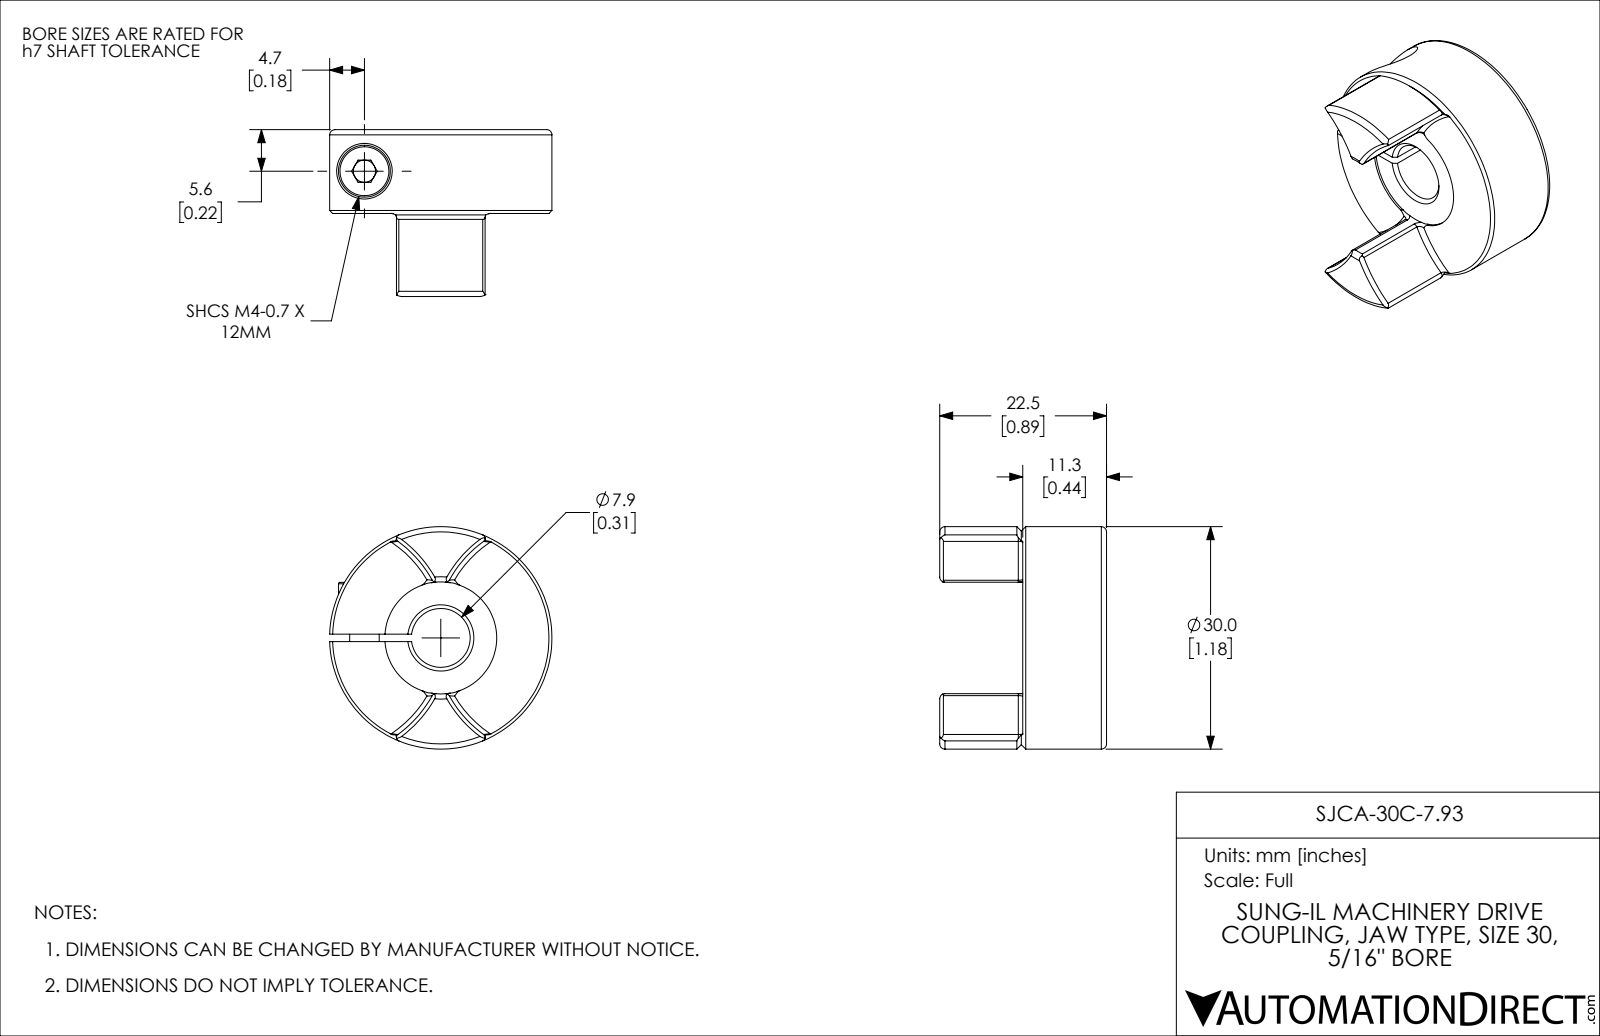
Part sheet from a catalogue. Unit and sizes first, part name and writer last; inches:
Units: inches
Overall size (bounding box): 1.181 × 1.181 × 0.886
Round holes (diameter × count): ⌀0.118 ×1, ⌀0.13 ×1, ⌀0.173 ×1, ⌀0.295 ×1, ⌀0.312 ×1, ⌀0.594 ×1
Round bosses / shafts (diameter × count): ⌀1.181 ×1, ⌀0.276 ×1, ⌀0.157 ×1
Partial cylindrical surfaces — rounded edges, fillets, slot ends (radius × count): R0.02 ×8, R0.634 ×2, R1.083 ×1
Main face-to-face distances: 0.445, 0.039, 0.433, 0.157, 0.441, 0.453, 0.886, 0.118, 0.315, 0.276
Volume: 0.499 in³ · Surface area: 6.391 in²
Bodies: 2 solids, 109 faces (27 planar, 41 cylindrical, 41 other)
Part name (STEP PRODUCT): SJCA-30C-7.93
STEP written by: SolidWorks 2021 (CONFIG_CONTROL_DESIGN)
